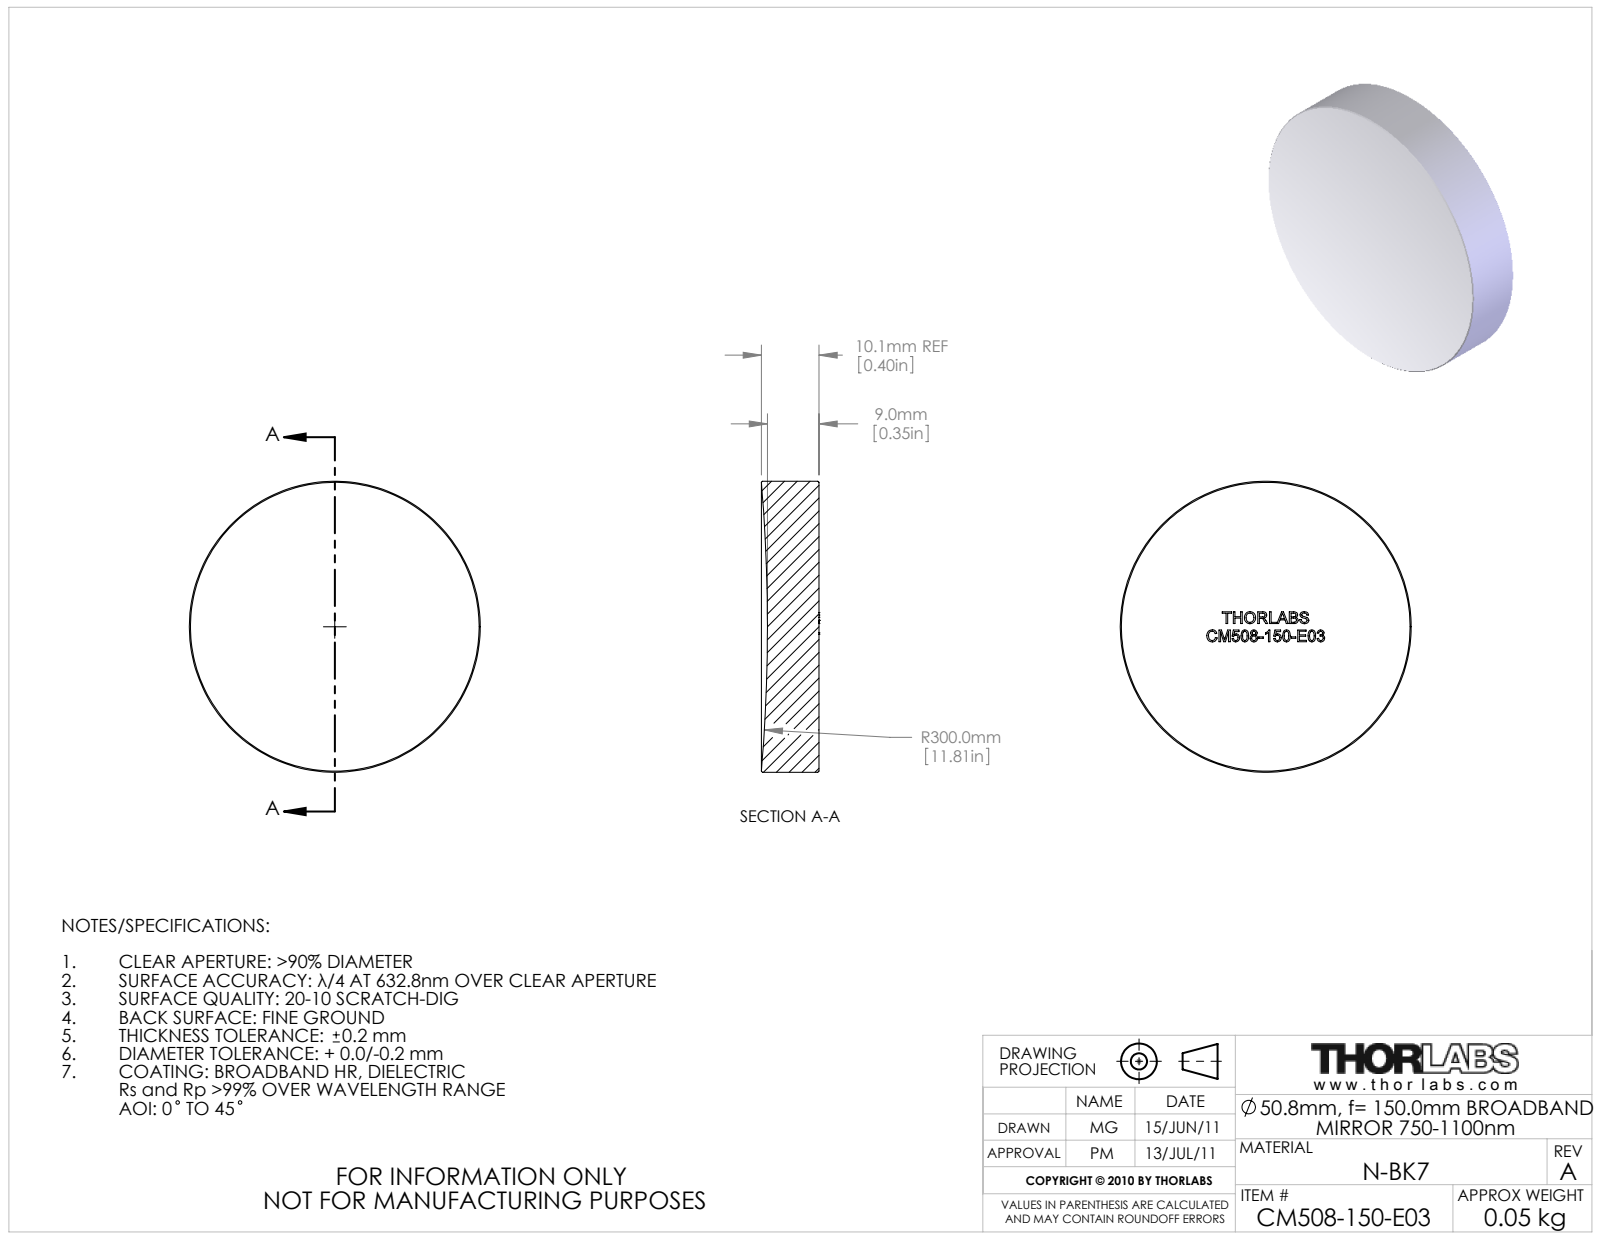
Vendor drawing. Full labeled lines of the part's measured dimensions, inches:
Part name (STEP PRODUCT): 22647-E0W
STEP written by: SolidWorks 2011 (AUTOMOTIVE_DESIGN)
Units: inches
Bodies: 0 solids, 44 faces (34 planar, 2 cylindrical, 8 other)
Overall size (bounding box): 2 × 2 × 0.396
Round bosses / shafts (diameter × count): ⌀2 ×1
